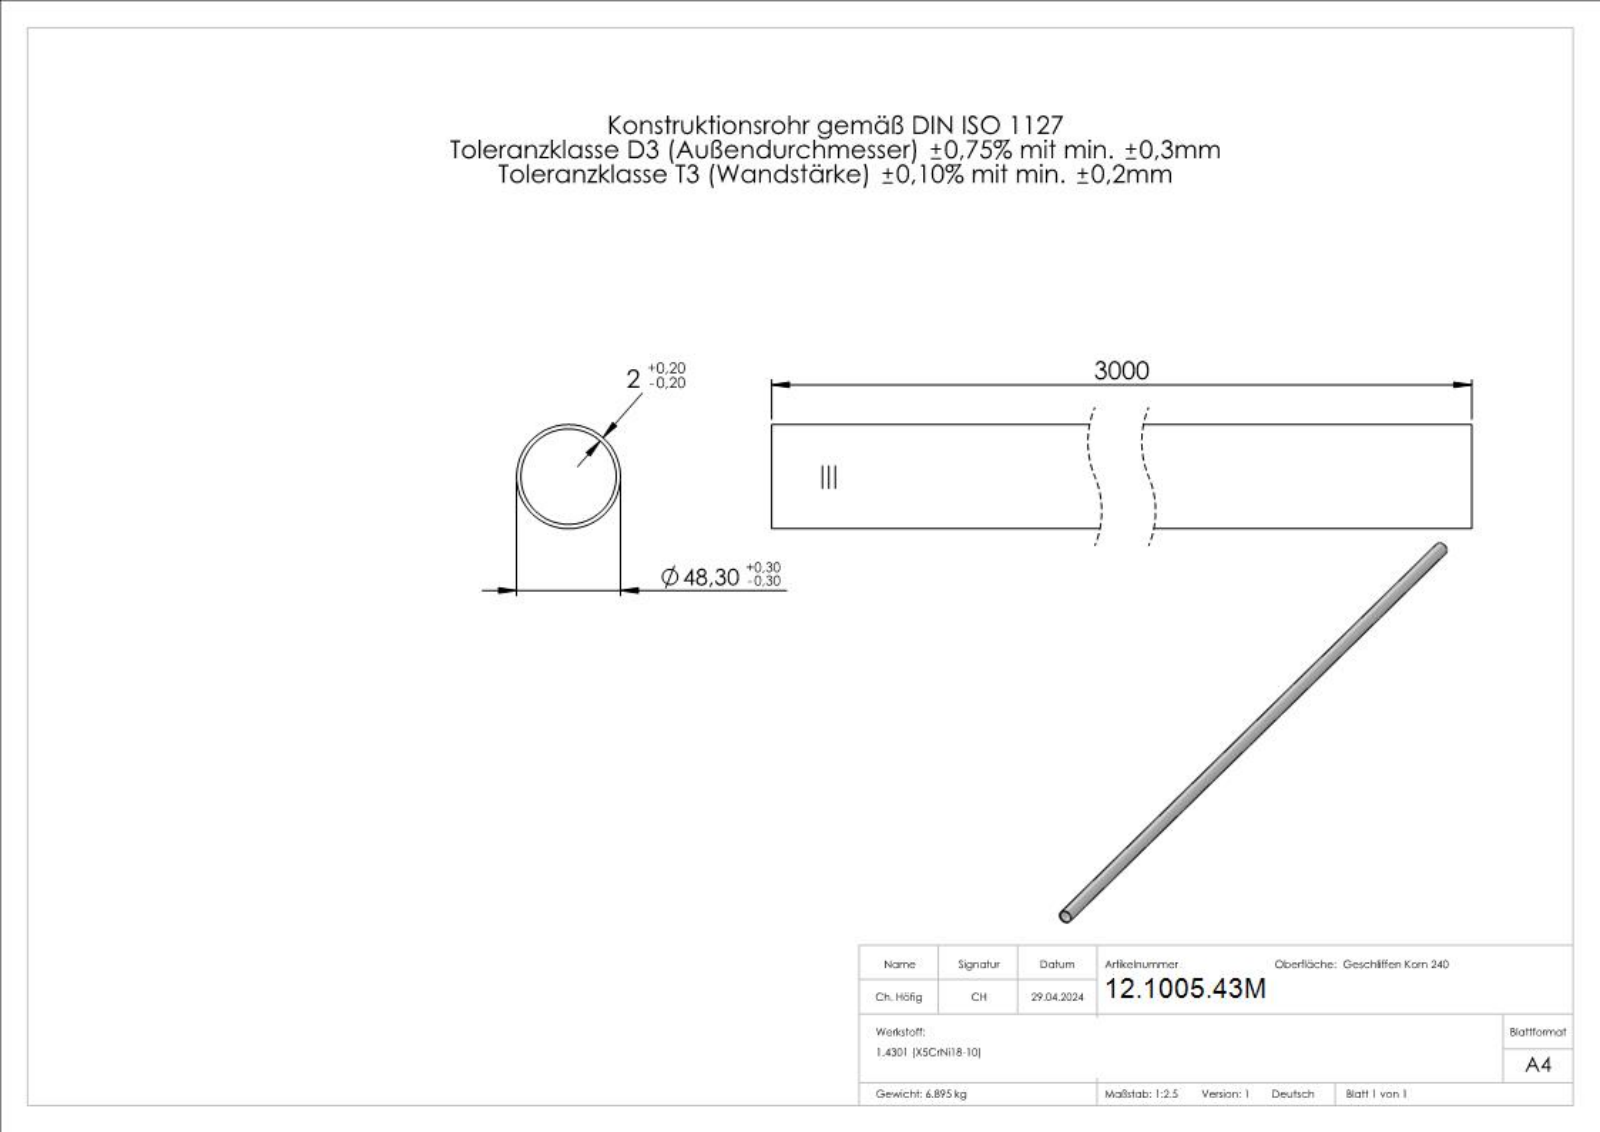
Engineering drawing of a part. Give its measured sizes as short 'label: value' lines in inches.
name: 55145-2403M
written by: SolidWorks 2018 (CONFIG_CONTROL_DESIGN)
unit: in
bodies: 1 solid, 303 faces (154 planar, 28 cylindrical, 121 other)
size: 118.11 × 1.902 × 1.902
volume: 53.26 in³; area: 1 354 in²
holes: 1× ⌀1.744
bosses: 1× ⌀1.902
rounds: 1× R0.876
face distances: 118.11, 0.031, 0.021, 0.062, 0.095, 0.029, 0.103, 0.063, 0.026, 0.088
